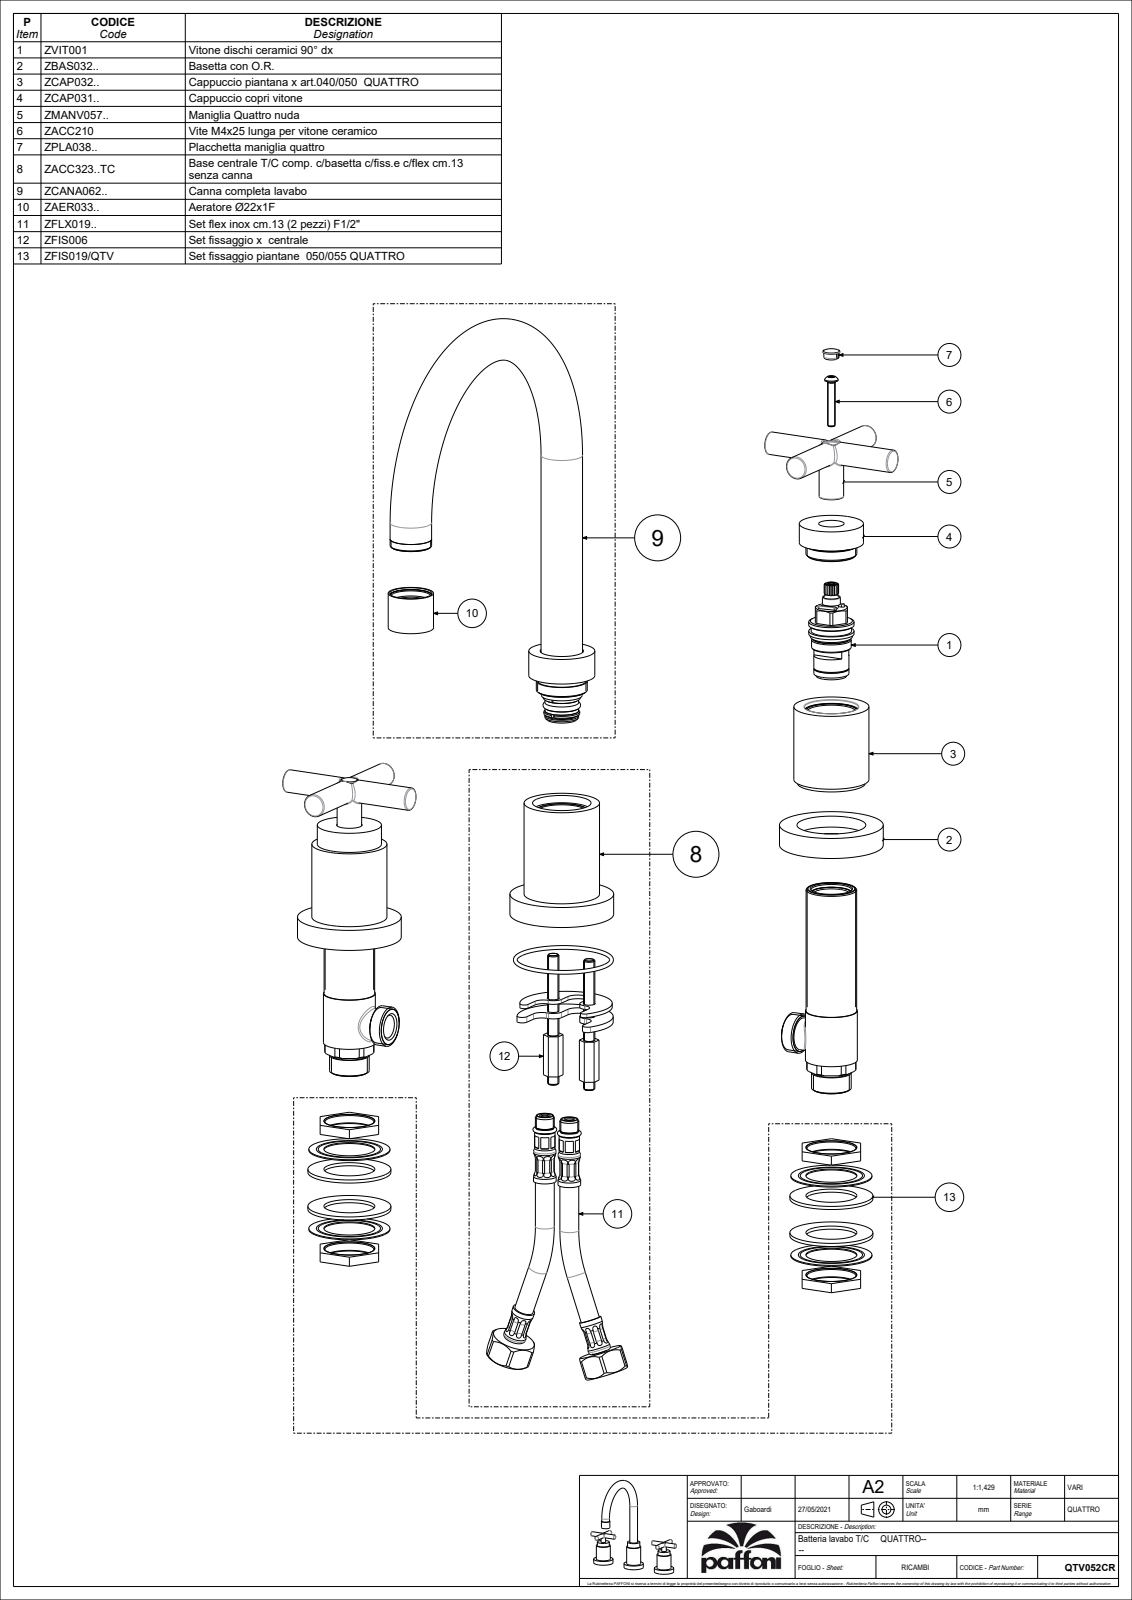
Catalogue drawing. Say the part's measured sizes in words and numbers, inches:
The part is named "QTV052CR". Its 3-D file was written by "CREO PARAMETRIC BY PTC INC, 2020044 (CONFIG_CONTROL_DESIGN)". It is 8 solids with 2522 faces: 1948 planar, 334 cylindrical and 240 other. Overall it measures 10.827 by 10.677 by 8.248 inches. Its volume is 17.74 cubic inches and its surface area 228.1 square inches. Round holes: 4 of diameter 0.177, 4 of diameter 0.748, 3 of diameter 0.276, 3 of diameter 0.787, 3 of diameter 1.004, 3 of diameter 1.437, 3 of diameter 1.85, 3 of diameter 2.087, 2 of diameter 0.13, 2 of diameter 0.207, 2 of diameter 0.315, 2 of diameter 0.346. Round bosses or shafts: 3 of diameter 2.165, 3 of diameter 1.929, 3 of diameter 1.417, 3 of diameter 0.945, 3 of diameter 0.472, 2 of diameter 1.567, 2 of diameter 1.339, 2 of diameter 1.055. Partial cylindrical surfaces (rounded edges, fillets, slot ends): 34 of radius 0.004, 4 of radius 0.02, 4 of radius 0.039, 2 of radius 0.118, 2 of radius 0.37. The main face-to-face distances are 0.433, 0.197, 0.236, 2.224, 1.988, 0.079, 0.157, 0.354, 2.421, 2.067. The hole center spacings are 0.355, 0.585, 0.606, 0.938, 3.526, 3.647, 3.937, 4.237.
